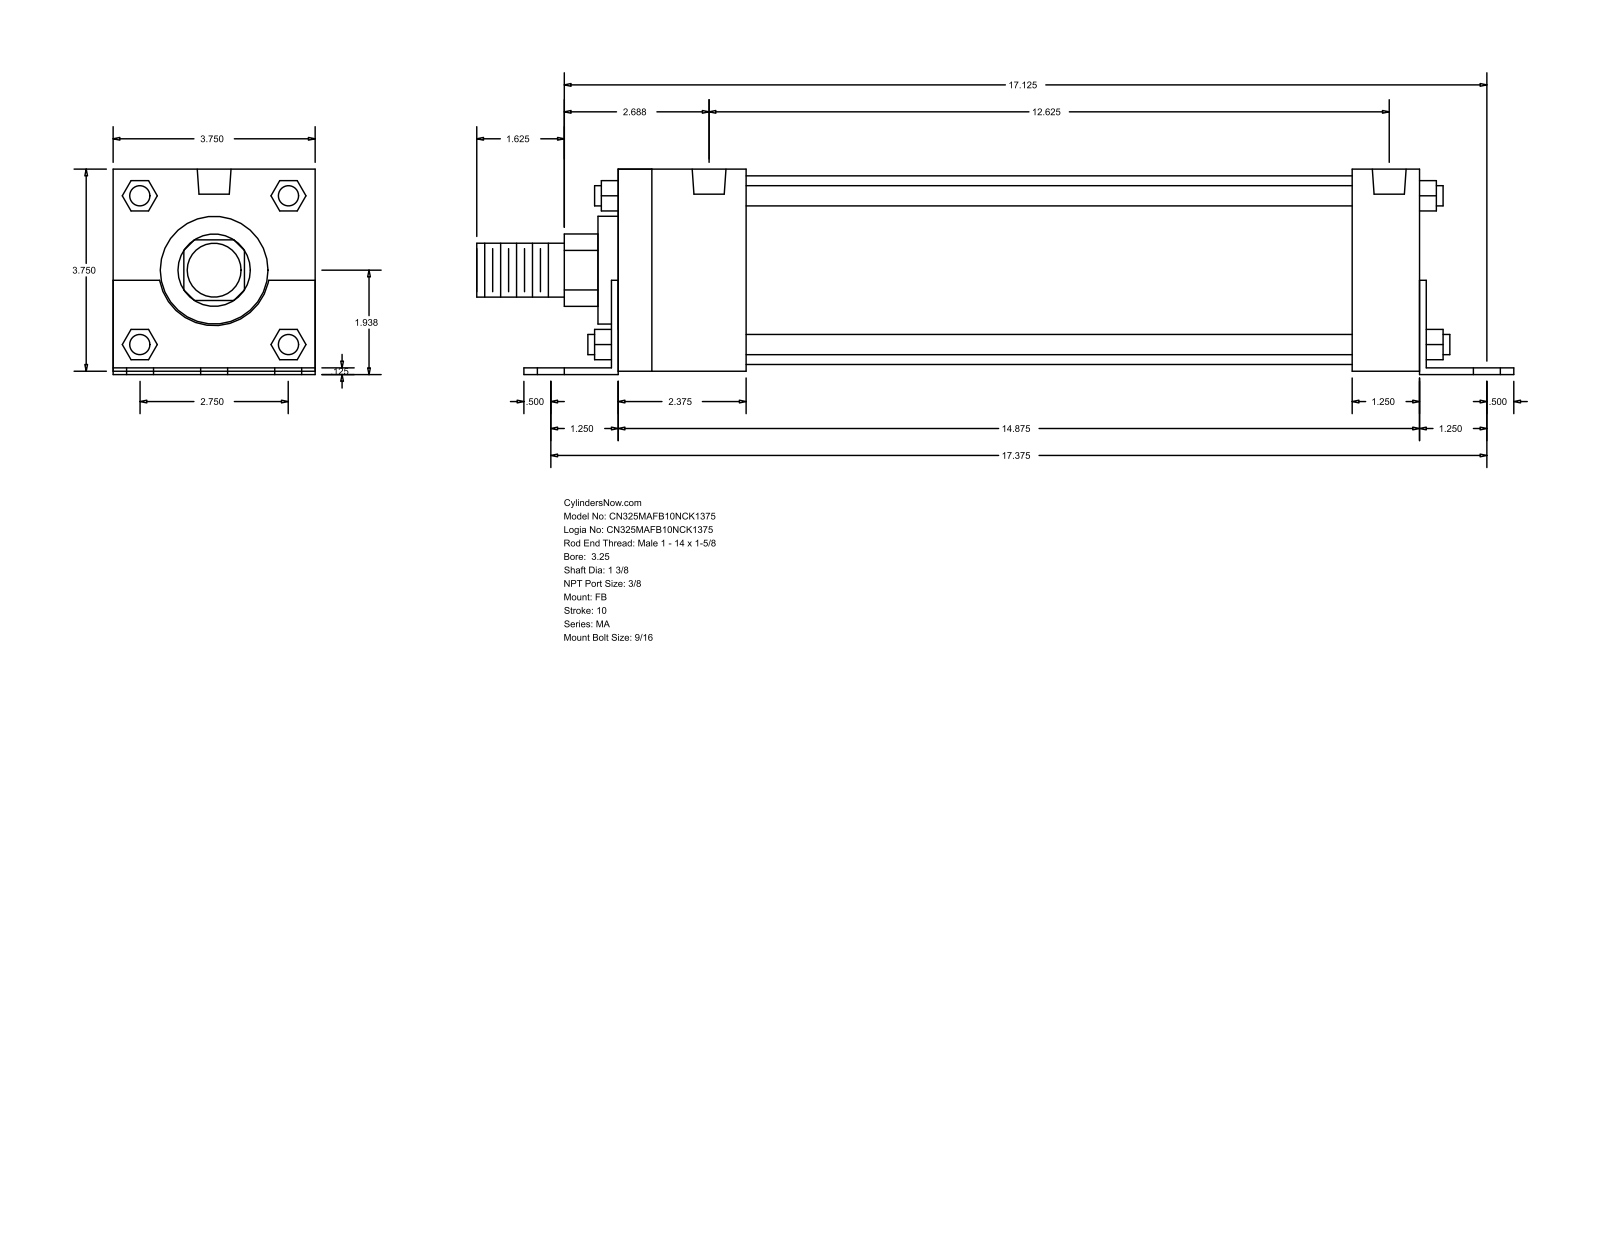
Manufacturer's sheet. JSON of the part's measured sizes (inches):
{"part_name": "MA_FB__0325_1.375", "step_written_by": "GSSL Pune (CONFIG_CONTROL_DESIGN)", "units": "inches", "bodies": {"solids": 0, "faces": 140, "planar": 105, "cylindrical": 35, "other": 0}, "overall_size": [19.25, 3.813, 3.75], "round_holes": [[0.563, 6], [0.437, 4], [0.627, 2]], "round_bosses_or_shafts": [[0.375, 4], [3.5, 1], [2, 1], [1.375, 1], [1, 1]], "partial_cylinders_radius": [[0.672, 1], [1.03, 1]], "face_to_face_distances": [3.75, 0.125, 0.063, 3.812, 0.062, 3.687, 15, 14.875, 1.25, 1.375], "hole_center_spacings": [1.375, 17.43, 17.375, 2.275, 2.427, 2.75, 3.243, 3.414]}
